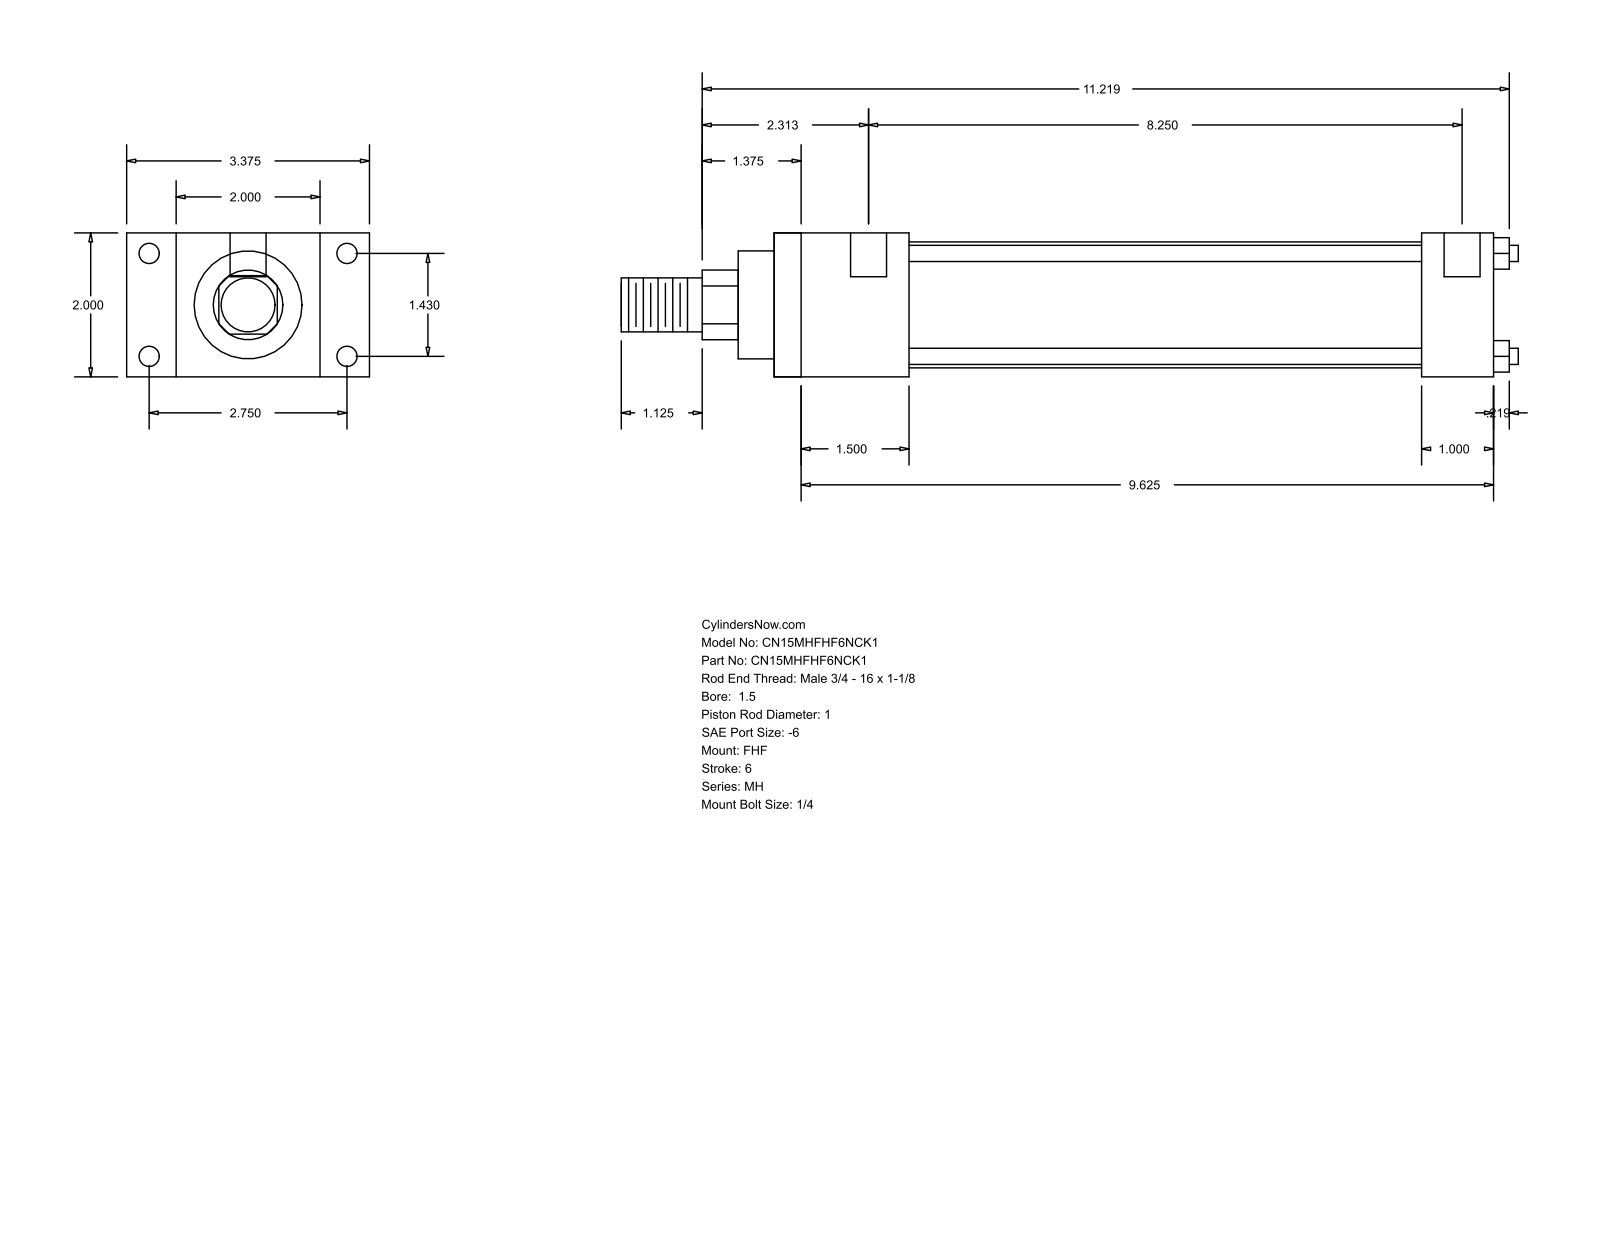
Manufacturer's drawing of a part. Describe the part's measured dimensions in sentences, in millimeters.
The part is named "MH_FHF__0150_1". Its 3-D file was written by "GSSL Pune (CONFIG_CONTROL_DESIGN)". It is 0 solids with 88 faces: 60 planar, 28 cylindrical and 0 other. Overall it measures 316.71 by 85.72 by 50.8 millimeters. Round holes: 4 of diameter 5.56, 4 of diameter 7.14, 2 of diameter 12.7. Round bosses or shafts: 4 of diameter 5.71, 1 of diameter 44.45, 1 of diameter 38.1, 1 of diameter 25.4, 1 of diameter 19.05. Partial cylindrical surfaces (rounded edges, fillets, slot ends): 1 of radius 12.29. The main face-to-face distances are 50.8, 17.46, 68.26, 47.63, 85.72, 254, 206.37, 25.4, 228.6, 180.97. The hole center spacings are 36.32, 69.84, 78.72, 212.73, 3.18, 209.55.
